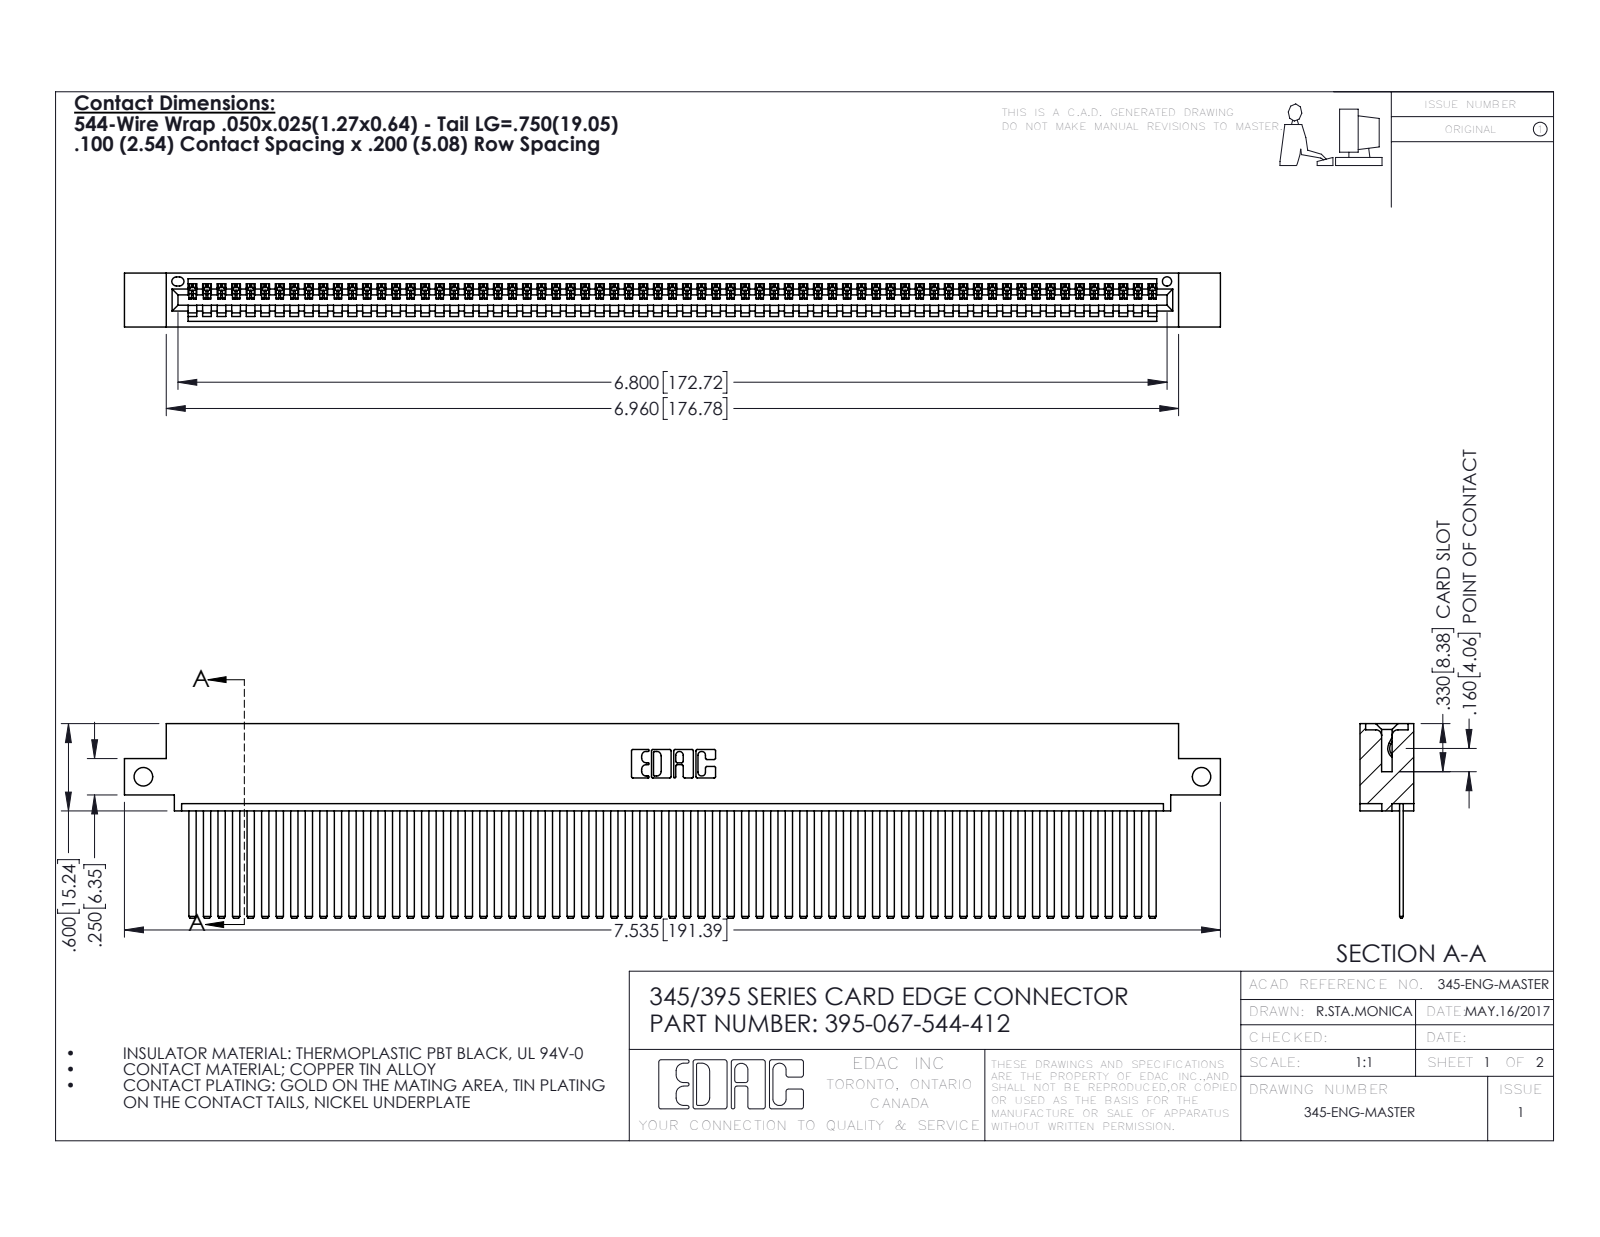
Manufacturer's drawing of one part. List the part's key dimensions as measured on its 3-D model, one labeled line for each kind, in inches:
Part name (STEP PRODUCT): 345-292-001_345-293-144; 395-067-544-412; 345 Part_0.110 Offset - Side Mount
STEP written by: SolidWorks 2016 (CONFIG_CONTROL_DESIGN)
Units: inches
Bodies: 68 solids, 3614 faces (2496 planar, 1118 cylindrical, 0 other)
Overall size (bounding box): 7.535 × 1.337 × 0.37
Volume: 1.159 in³ · Surface area: 43.18 in²
Round holes (diameter × count): ⌀0.128 ×2, ⌀0.064 ×1
Partial cylindrical surfaces — rounded edges, fillets, slot ends (radius × count): R0.006 ×134, R0.01 ×22, R0.007 ×6, R0.031 ×6, R0.026 ×3, R0.031 ×2, R0.04 ×2, R0.014 ×1
Main face-to-face distances: 0.072, 0.298, 0.025, 0.098, 0.272, 0.37, 0.2, 0.225, 0.149, 0.072
Hole centre spacings: 7.275
